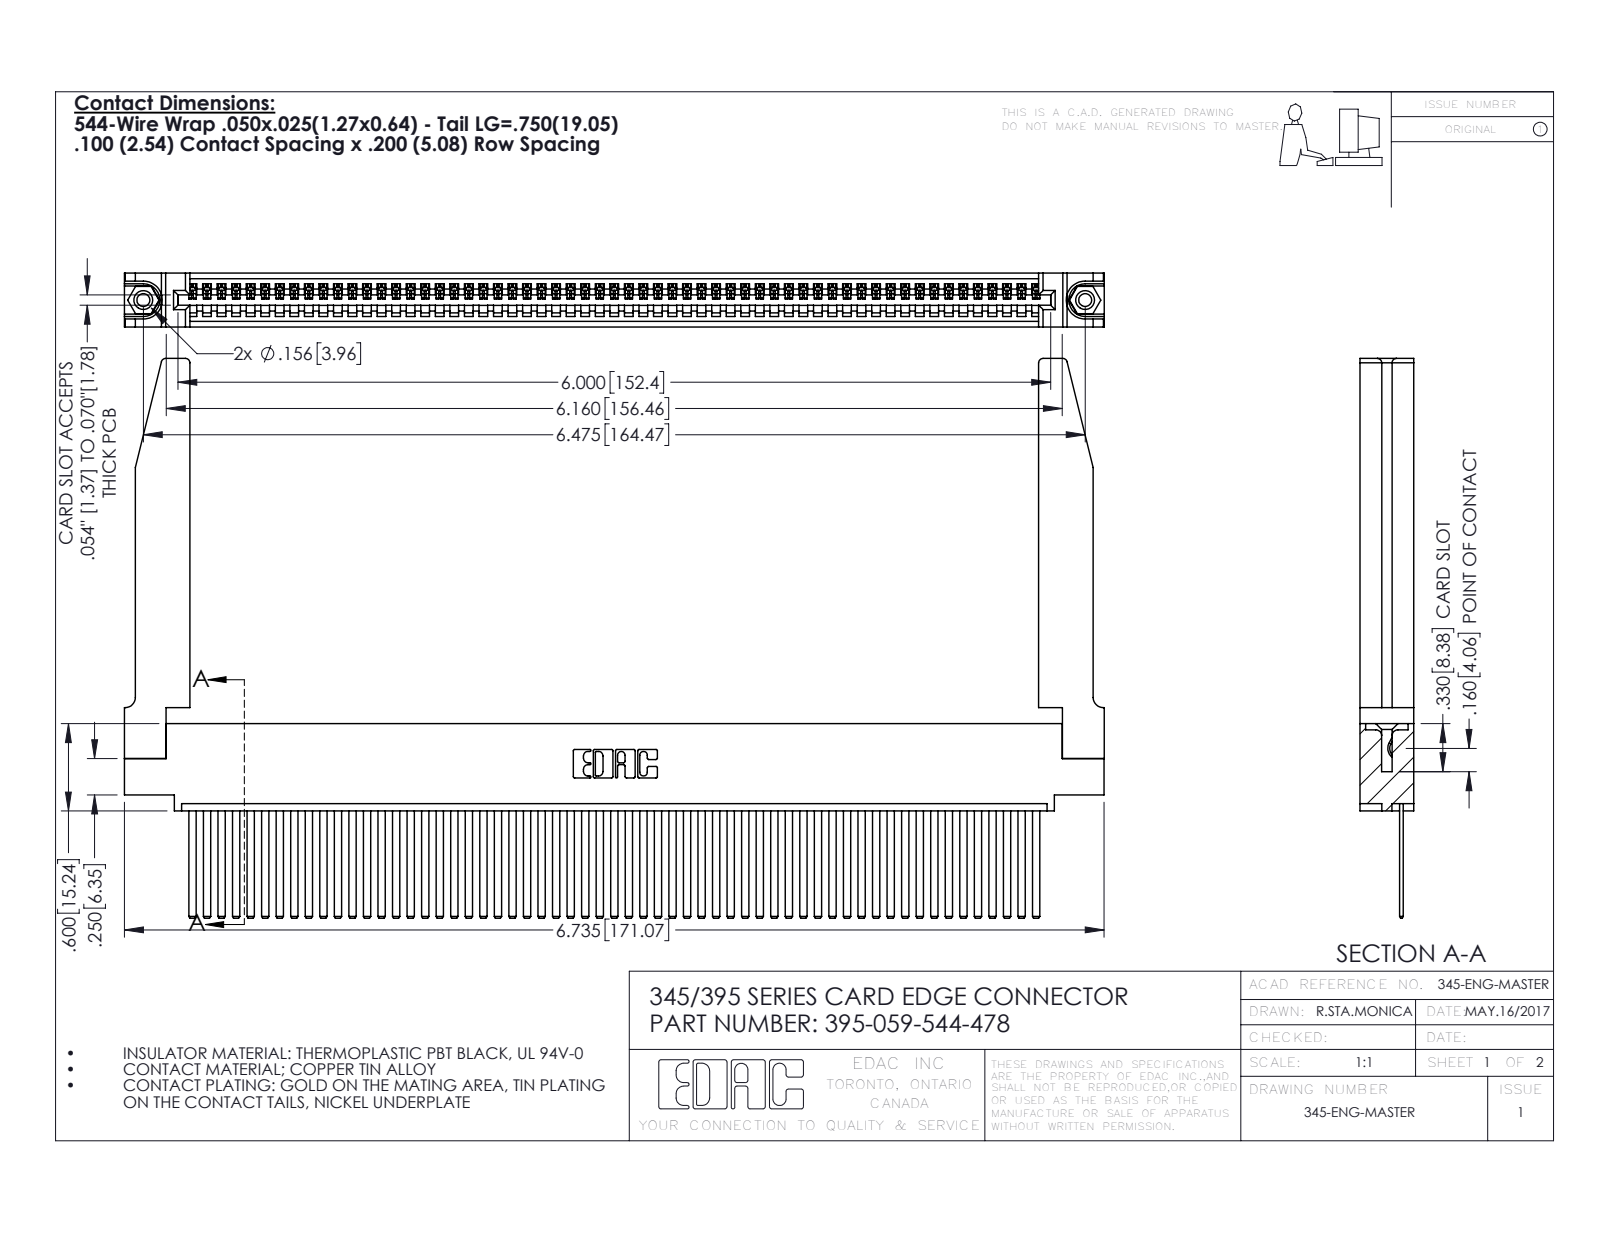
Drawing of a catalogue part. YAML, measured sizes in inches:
part_name: "345 Part_0.110 Offset - 0.156 Dia-TH; 395-059-544-478; 345-250-001_345-250-001-102; 345-292-001_345-293-144 (+1 more)"
step_written_by: "SolidWorks 2016 (CONFIG_CONTROL_DESIGN)"
units: inches
bodies: {solids: 64, faces: 3432, planar: 2350, cylindrical: 1030, other: 52}
overall_size: [6.736, 3.847, 0.37]
volume: 1.512
surface_area: 49.29
round_holes:
  - {diameter: 0.089, count: 2}
  - {diameter: 0.125, count: 2}
  - {diameter: 0.156, count: 2}
  - {diameter: 0.064, count: 1}
round_bosses_or_shafts:
  - {diameter: 0.155, count: 2}
partial_cylinders:
  - {radius: 0.006, count: 118}
  - {radius: 0.01, count: 22}
  - {radius: 0.03, count: 8}
  - {radius: 0.007, count: 6}
  - {radius: 0.031, count: 6}
  - {radius: 0.026, count: 3}
  - {radius: 0.031, count: 2}
  - {radius: 0.04, count: 2}
face_to_face_distances: [0.072, 0.298, 0.37, 0.098, 0.272, 0.025, 0.2, 0.225, 0.148, 0.15]
hole_center_spacings: [0.27, 6.239, 6.475]
